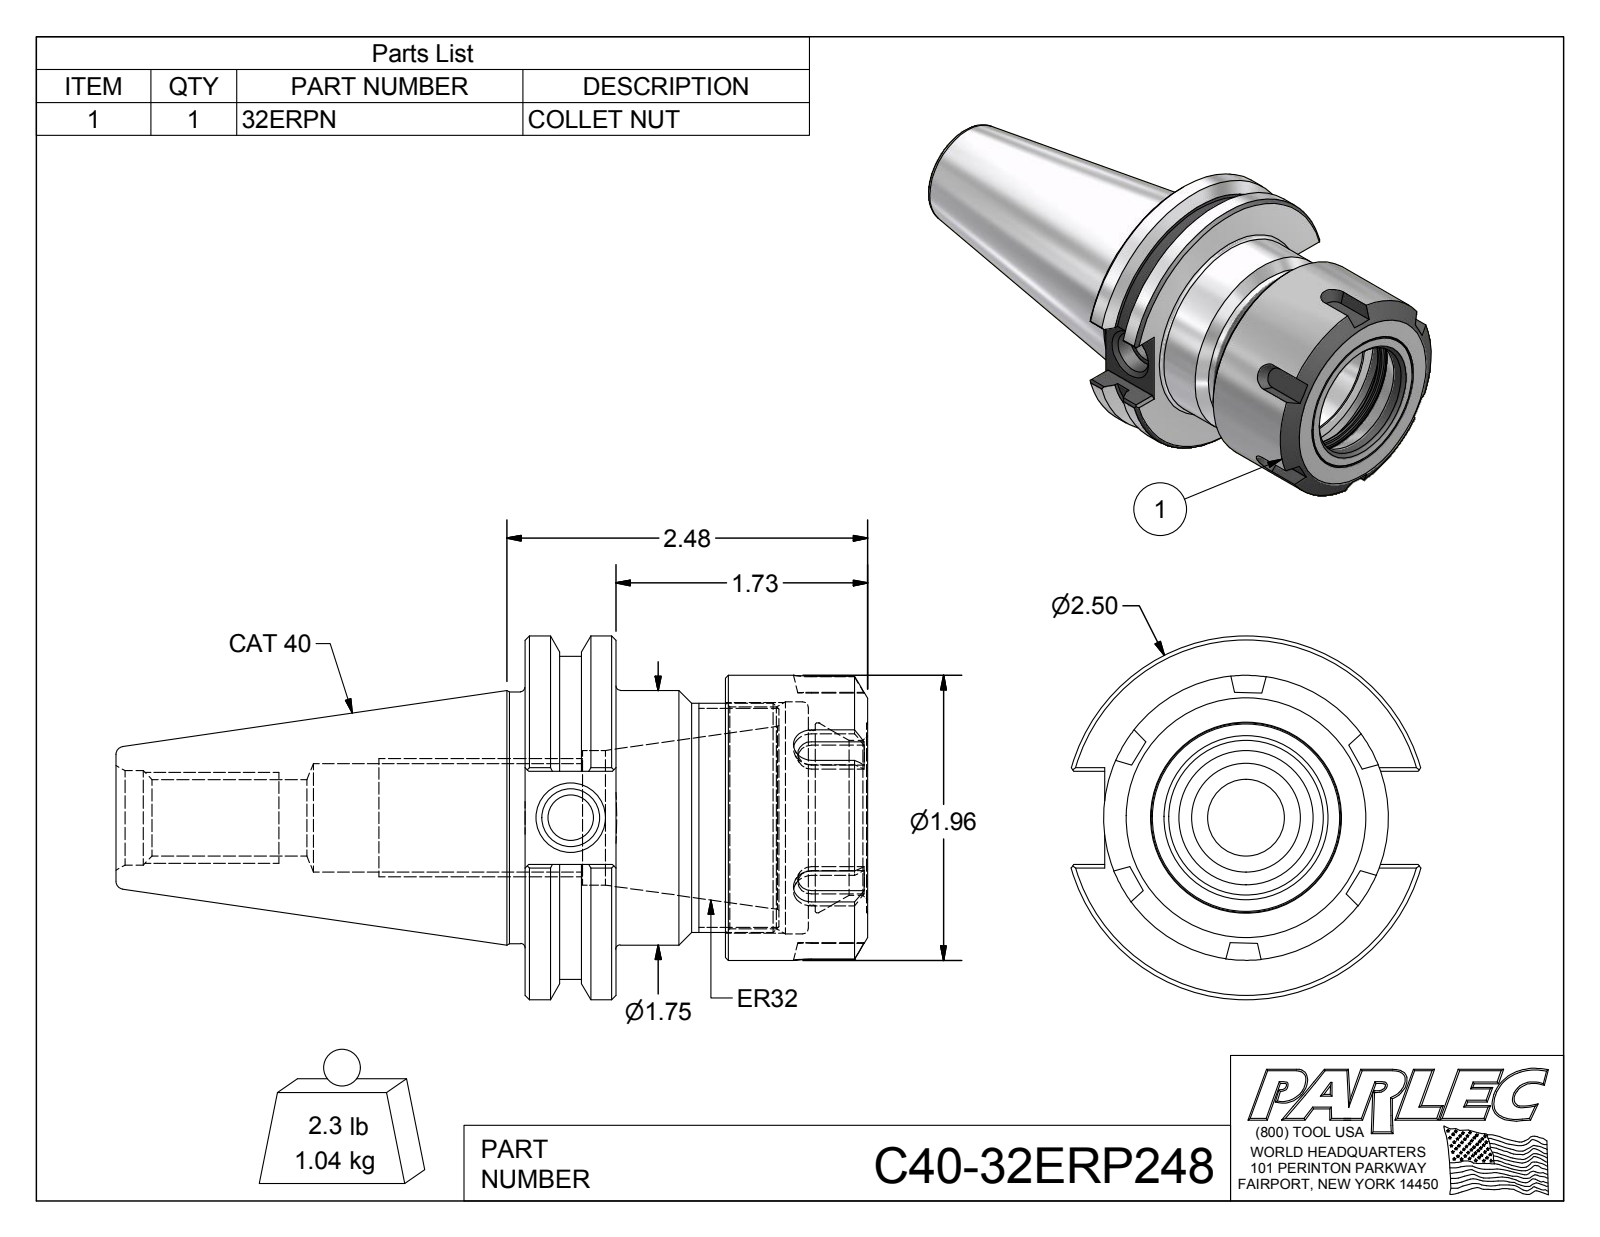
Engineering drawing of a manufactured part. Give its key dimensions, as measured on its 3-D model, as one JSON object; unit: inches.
{"part_name": "C40-32ERP248; C40-32ER236-1; 32ERPN", "step_written_by": "Autodesk Inventor 2012 (AUTOMOTIVE_DESIGN)", "units": "inches", "bodies": {"solids": 2, "faces": 117, "planar": 55, "cylindrical": 21, "other": 41}, "overall_size": [5.168, 2.5, 2.403], "volume_in3": 8.265, "surface_area_in2": 56, "round_holes": [[0.315, 1], [0.396, 1], [0.527, 1], [0.648, 1], [0.745, 1], [0.925, 1], [1.063, 1], [1.2, 1], [1.305, 1], [1.523, 1], [1.595, 1]], "round_bosses_or_shafts": [[2.5, 1], [2.219, 1], [1.958, 1], [1.75, 1], [1.73, 1], [1.575, 1]], "face_to_face_distances": [0.625, 2.355, 1.73, 1.377, 0.752, 0.978, 1.948, 1.323, 0.571, 0.407]}
